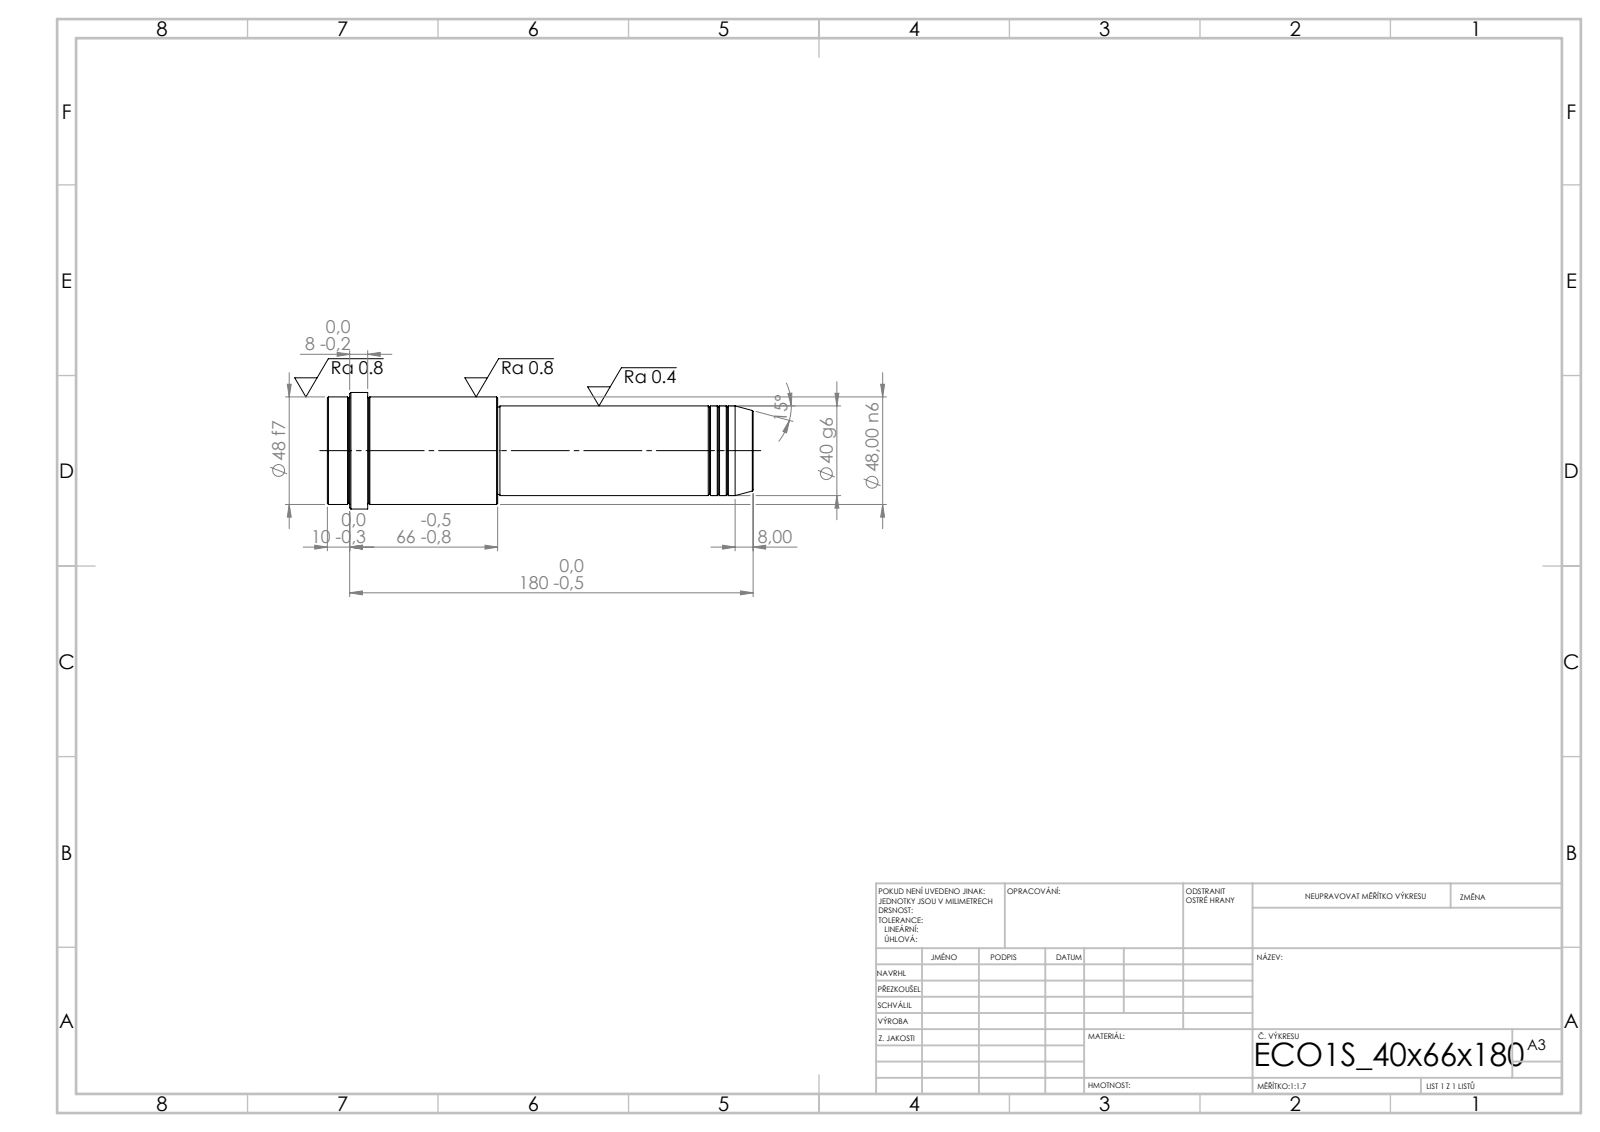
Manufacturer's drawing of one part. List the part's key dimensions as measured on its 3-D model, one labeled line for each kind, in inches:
STEP written by: SolidWorks 2019 (CONFIG_CONTROL_DESIGN)
Units: inches
Bodies: 1 solid, 52 faces (6 planar, 16 cylindrical, 30 other)
Overall size (bounding box): 7.48 × 2.047 × 2.047
Volume: 17.2 in³ · Surface area: 46.81 in²
Round bosses / shafts (diameter × count): ⌀2.047 ×1, ⌀1.89 ×1, ⌀1.575 ×1, ⌀1.535 ×1
Main face-to-face distances: 7.48, 4.488, 2.992, 6.772, 2.283, 0.709, 7.087, 2.598, 0.315, 0.394
